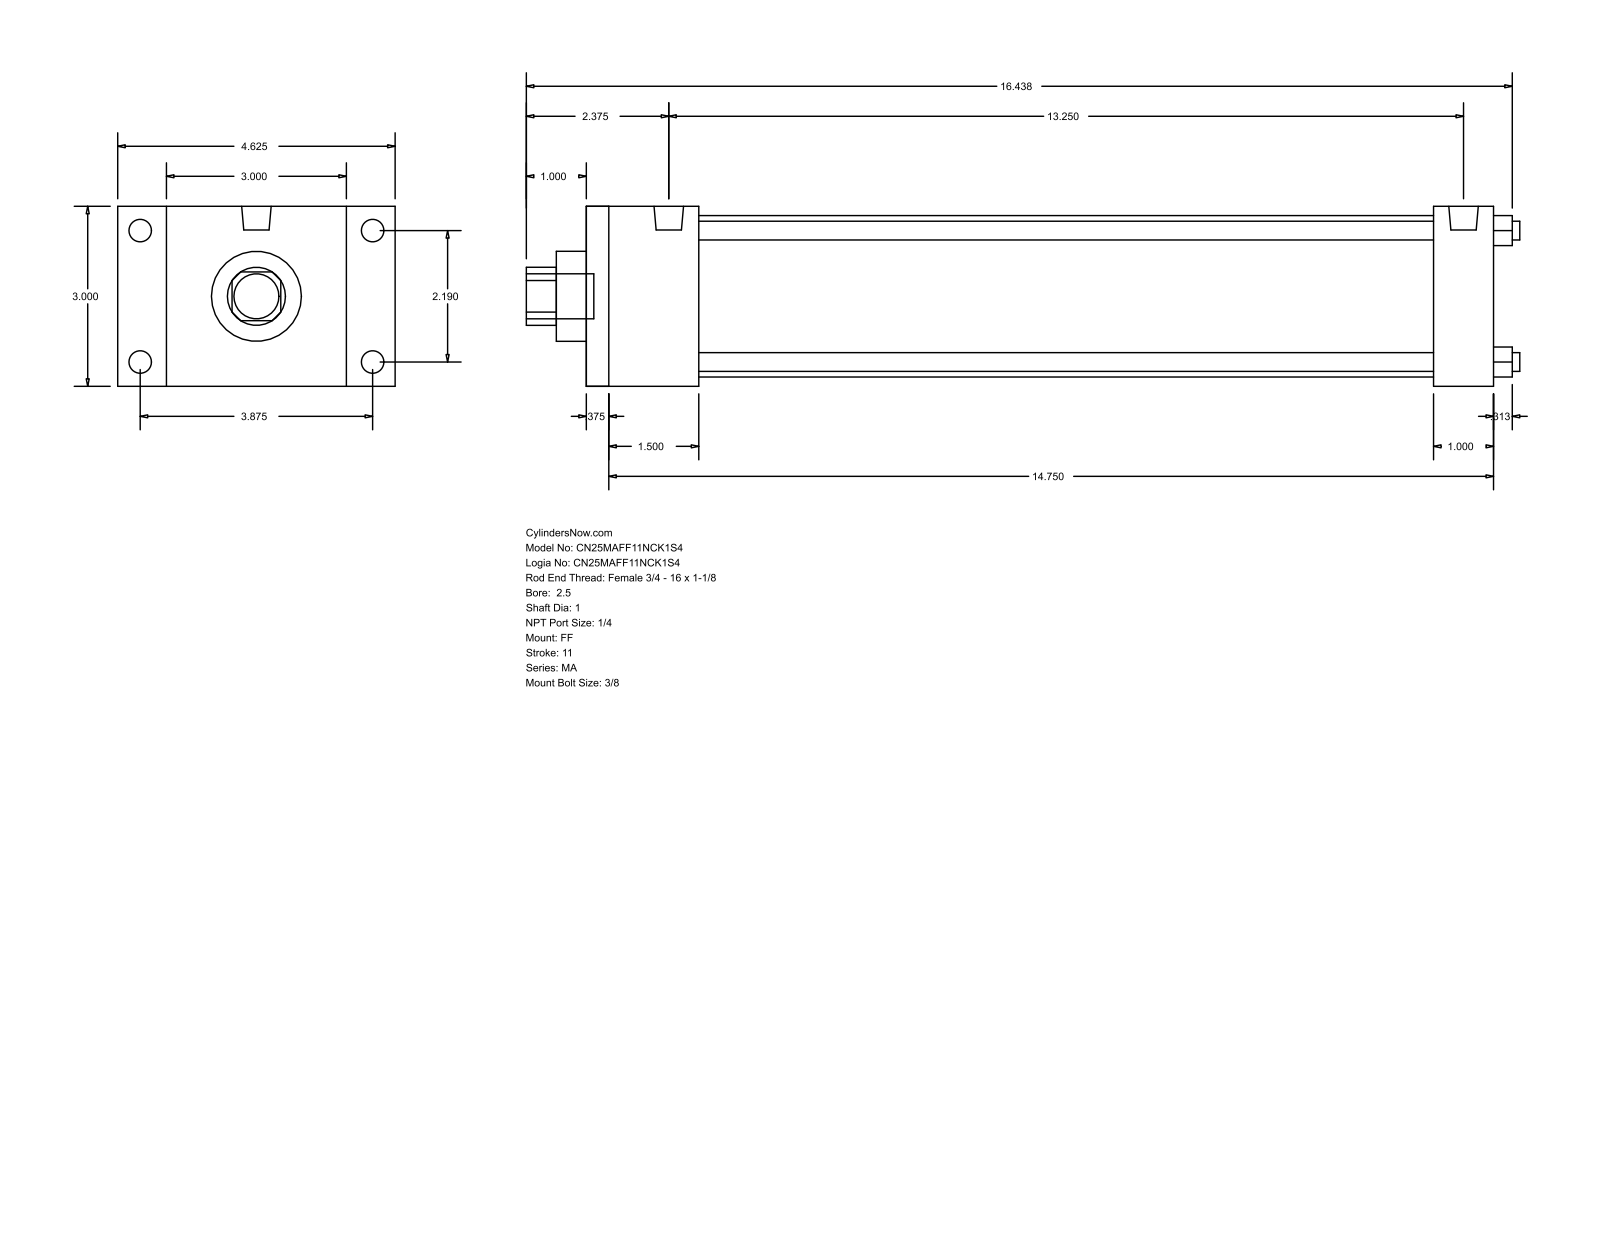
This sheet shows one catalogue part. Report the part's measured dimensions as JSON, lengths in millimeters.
{"part_name": "MA_FF__0250_1", "step_written_by": "GSSL Pune (CONFIG_CONTROL_DESIGN)", "units": "millimeters", "bodies": {"solids": 0, "faces": 92, "planar": 64, "cylindrical": 28, "other": 0}, "overall_size": [420.69, 117.47, 76.2], "round_holes": [[7.94, 4], [25.4, 1], [38.1, 1], [68.33, 1]], "round_bosses_or_shafts": [[9.53, 4], [7.94, 4], [12.49, 2], [19.05, 1]], "partial_cylinders_radius": [[12.29, 1]], "face_to_face_distances": [76.2, 384.17, 374.65, 9.52, 25.39, 47.63, 358.78, 38.11, 349.26, 311.15], "hole_center_spacings": [39.33, 55.62, 78.66]}
